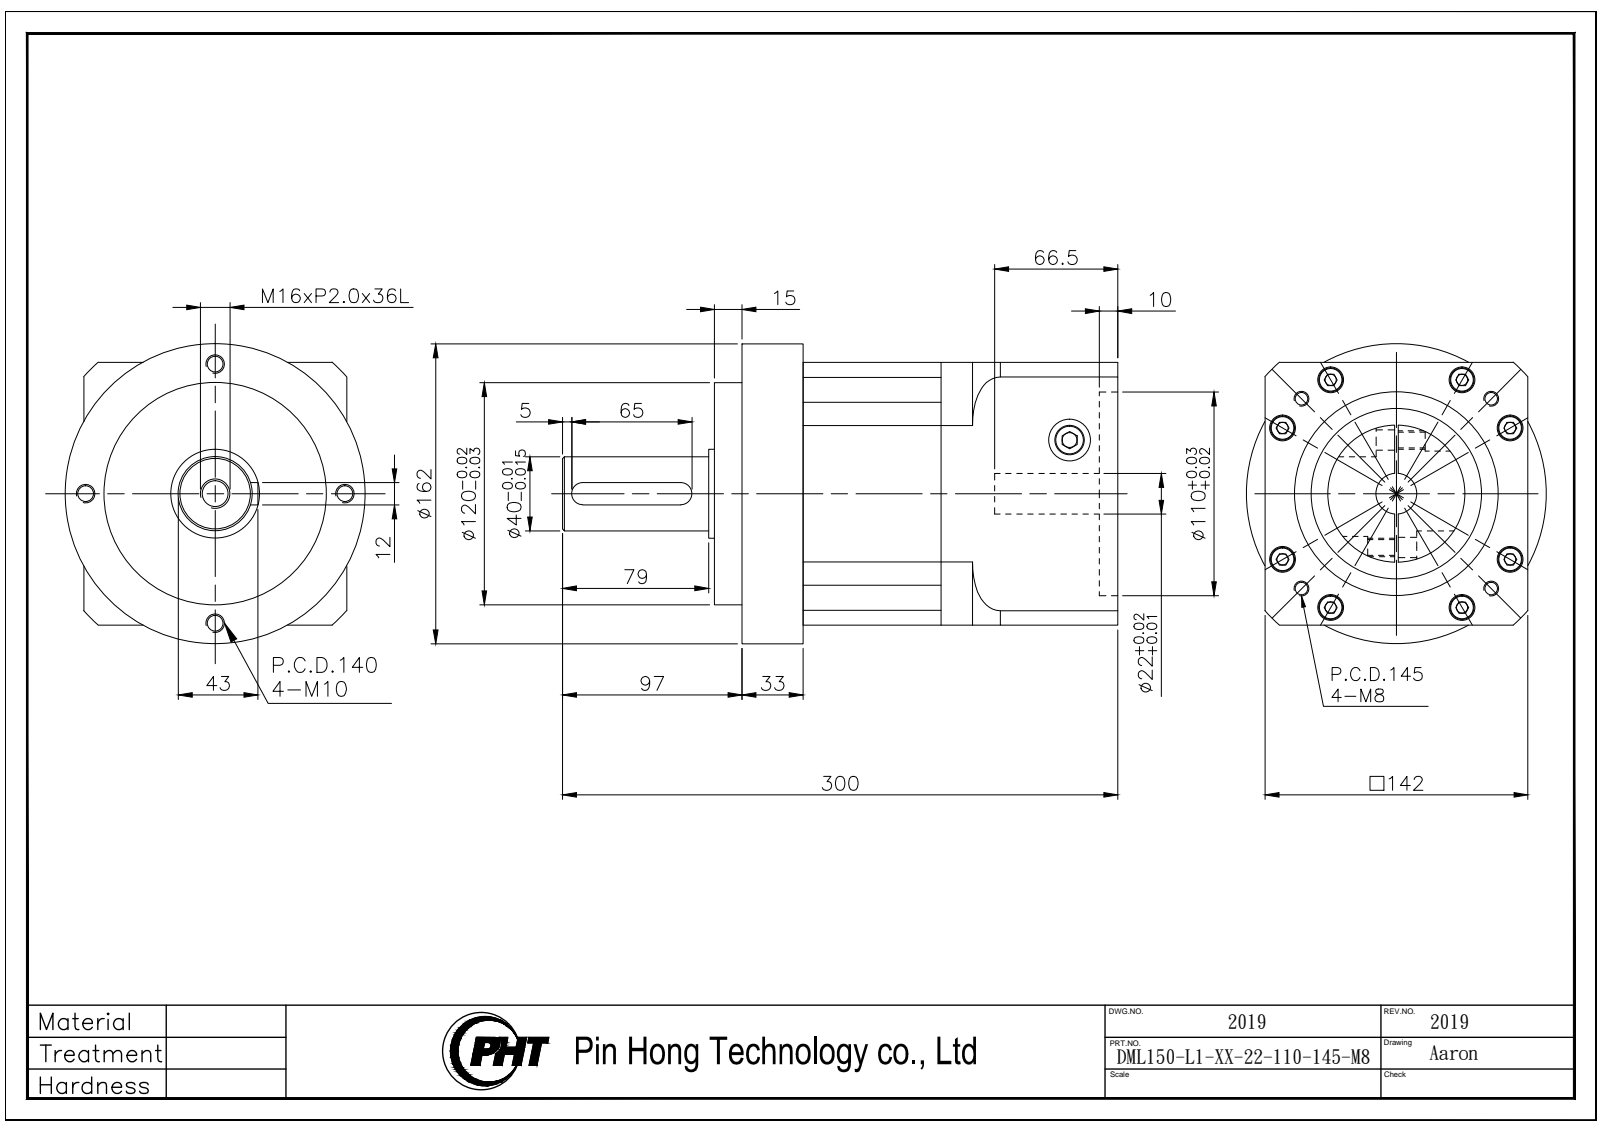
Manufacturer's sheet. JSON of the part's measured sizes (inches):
{"part_name": "DML150-L1-XX-22-110-145-M8_2019", "step_written_by": "SolidWorks 2016 (AUTOMOTIVE_DESIGN)", "units": "inches", "bodies": {"solids": 3, "faces": 263, "planar": 108, "cylindrical": 115, "other": 40}, "overall_size": [11.811, 6.378, 6.378], "volume_in3": 231.5, "surface_area_in2": 496.7, "round_holes": [[0.551, 9], [0.354, 8], [0.268, 4], [0.335, 4], [0.886, 2], [0.866, 1], [3.622, 1], [4.331, 1]], "round_bosses_or_shafts": [[0.512, 8], [6.378, 1], [4.724, 1], [2.913, 1], [1.89, 1], [1.575, 1]], "partial_cylinders_radius": [[0.394, 4], [0.236, 2], [3.15, 1], [3.74, 1]], "face_to_face_distances": [2.933, 5.591, 1.89, 4.823, 3.76, 6.693, 8.583, 7.992, 4.232, 1.299], "hole_center_spacings": [2.795, 0.74, 1.437, 2.149, 2.776, 3.44, 3.953, 4.483]}
